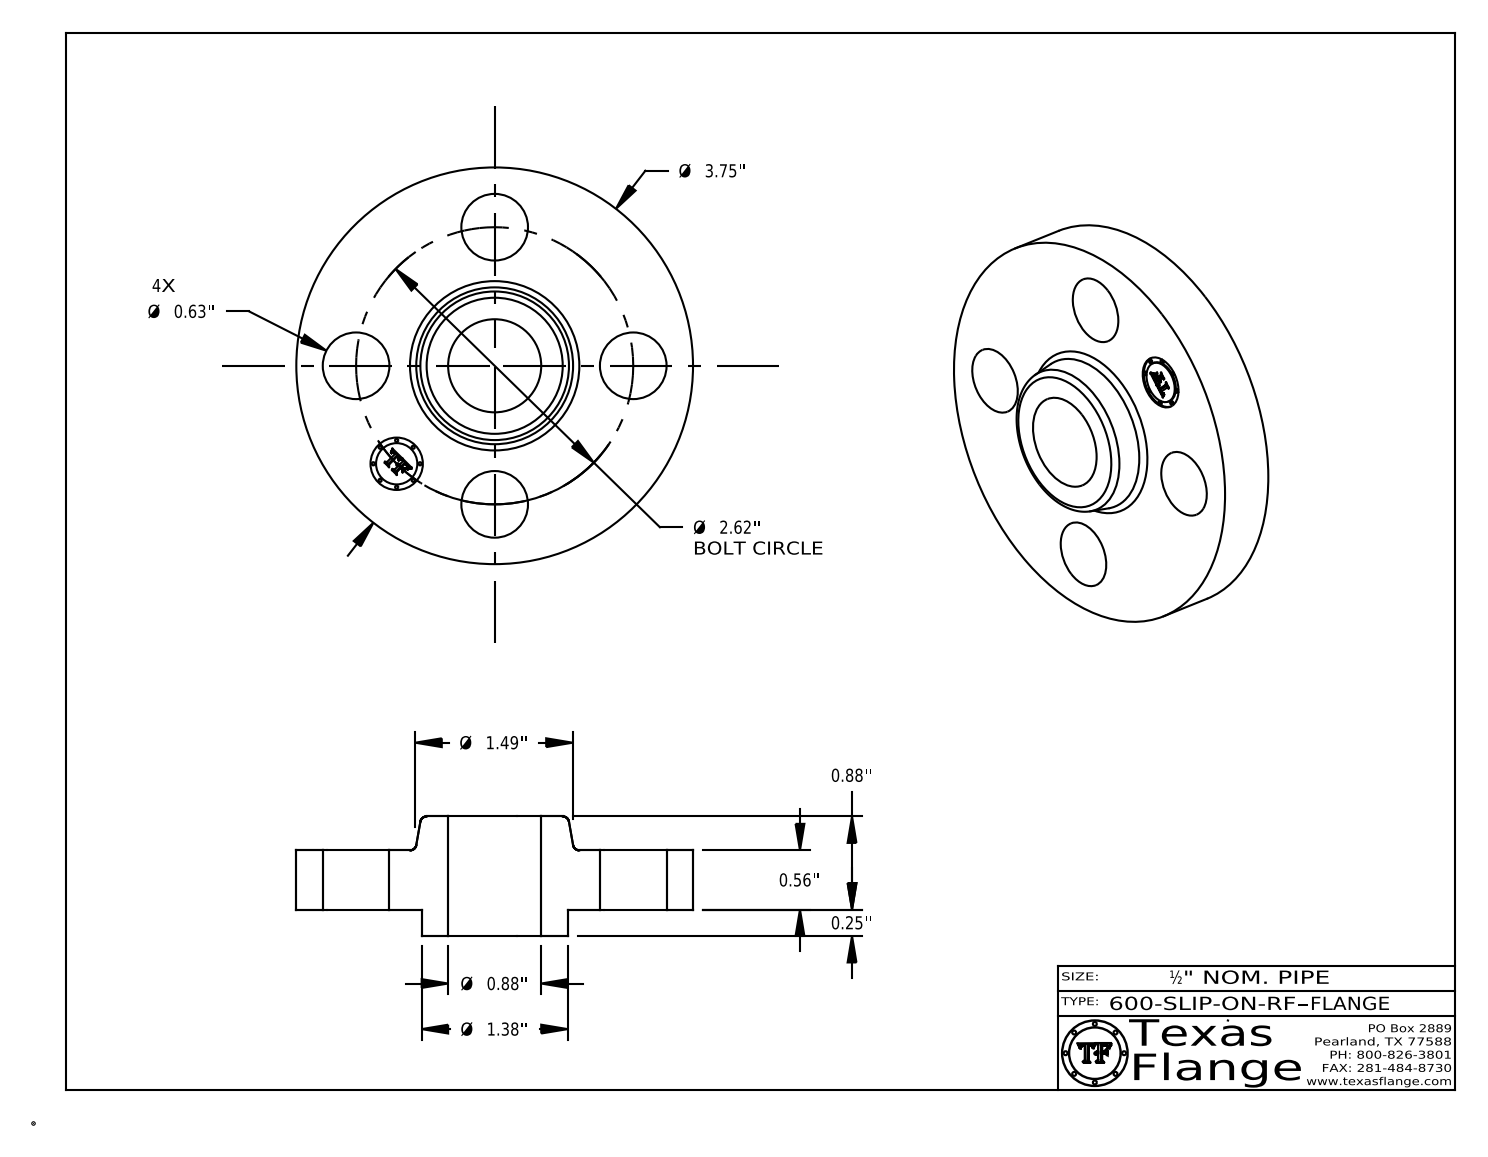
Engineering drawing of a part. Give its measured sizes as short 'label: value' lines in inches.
name: 600-SLIP-ON-RF
written by: CATIA V5 STEP AP214 (AUTOMOTIVE_DESIGN)
unit: in
bodies: 1 solid, 409 faces (369 planar, 34 cylindrical, 6 other)
size: 3.75 × 3.75 × 1.13
volume: 5.696 in³; area: 34.78 in²
holes: 4× ⌀0.63, 1× ⌀0.495, 1× ⌀0.88
bosses: 8× ⌀0.03, 1× ⌀3.75, 1× ⌀1.38, 1× ⌀0.39
face distances: 0.56, 0.25, 0.81, 1.13, 0.88, 0.32, 0.795, 0.545, 0.015, 0.335
hole spacings: 1.31, 1.852, 1.003, 2.42, 2.62, 1.31
